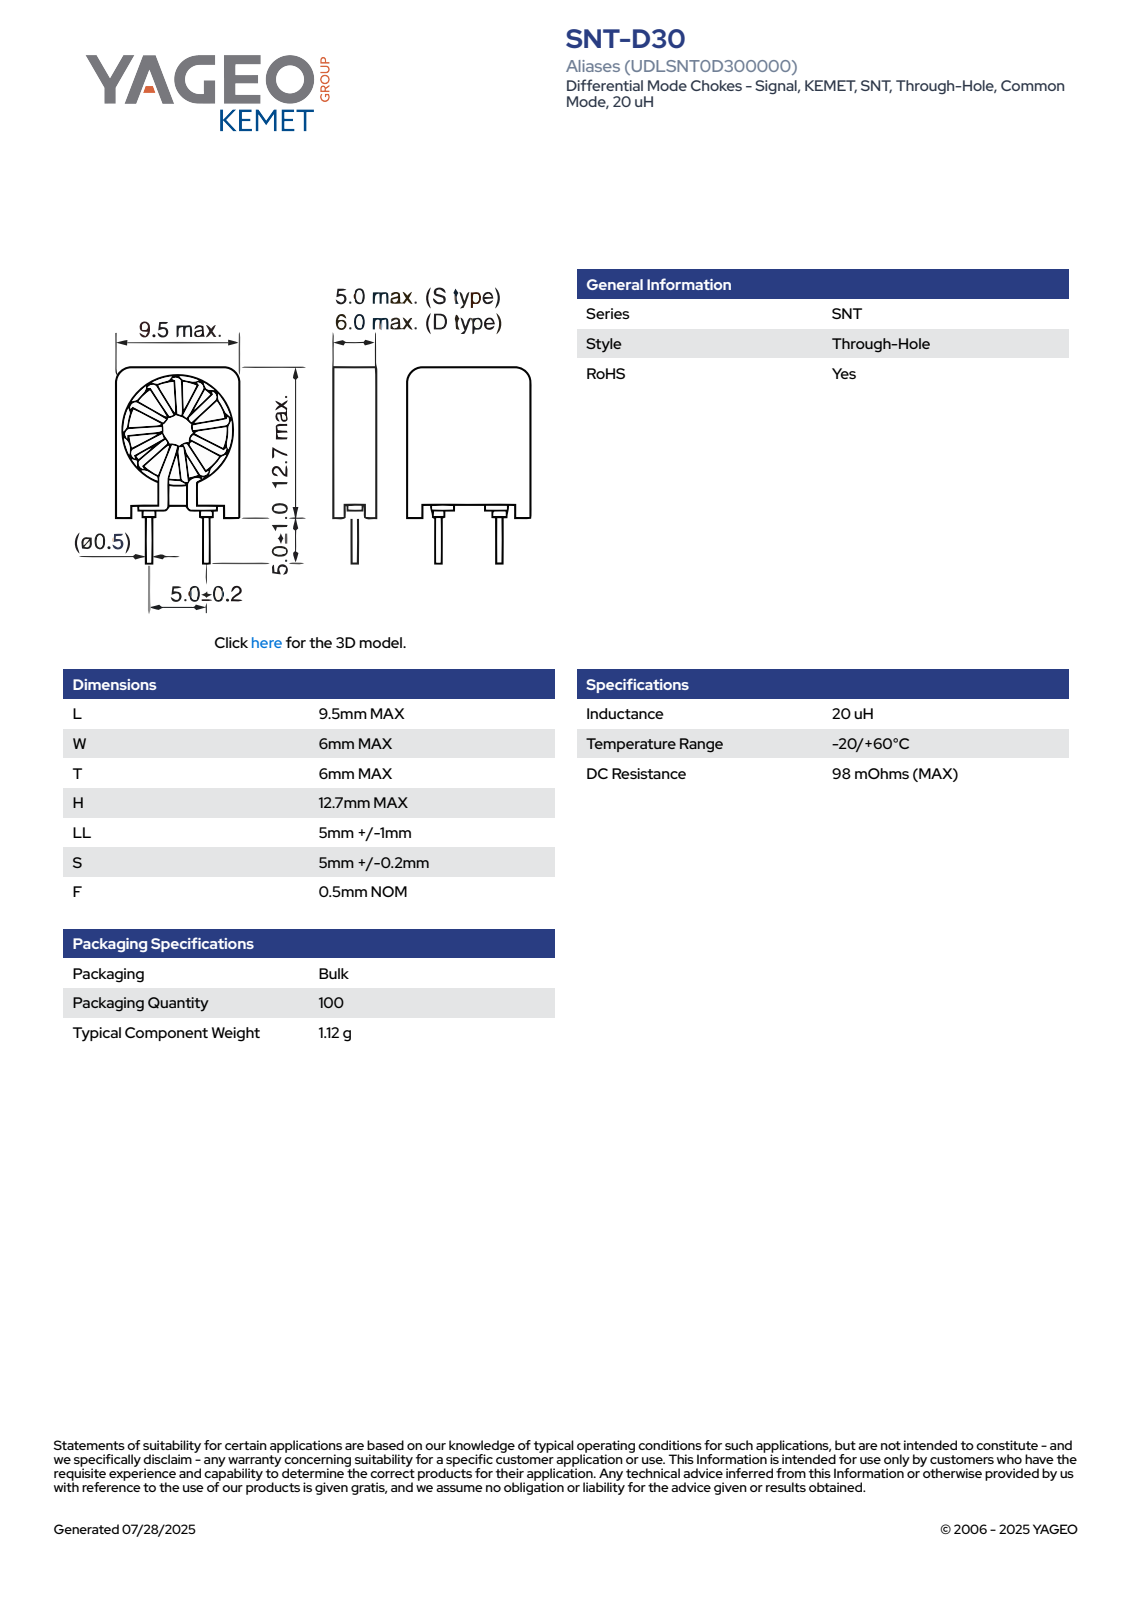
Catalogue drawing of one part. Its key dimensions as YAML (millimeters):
part_name: "IFC_NTSNT_L9.5W6T6"
step_written_by: "SolidWorks 2014 (AUTOMOTIVE_DESIGN)"
units: millimeters
bodies: {solids: 1, faces: 498, planar: 214, cylindrical: 199, other: 85}
overall_size: [18.7, 9.5, 6]
volume: 632
surface_area: 718
round_holes:
  - {diameter: 2.37, count: 1}
  - {diameter: 8.51, count: 1}
round_bosses_or_shafts:
  - {diameter: 0.5, count: 2}
  - {diameter: 7.39, count: 1}
  - {diameter: 1.76, count: 1}
partial_cylinders:
  - {radius: 0.52, count: 32}
  - {radius: 0.62, count: 32}
  - {radius: 0.25, count: 20}
  - {radius: 0.5, count: 2}
face_to_face_distances: [9.5, 6, 12, 3.5, 2.5, 5.8, 2.3, 4.04, 1.07, 2.97]
